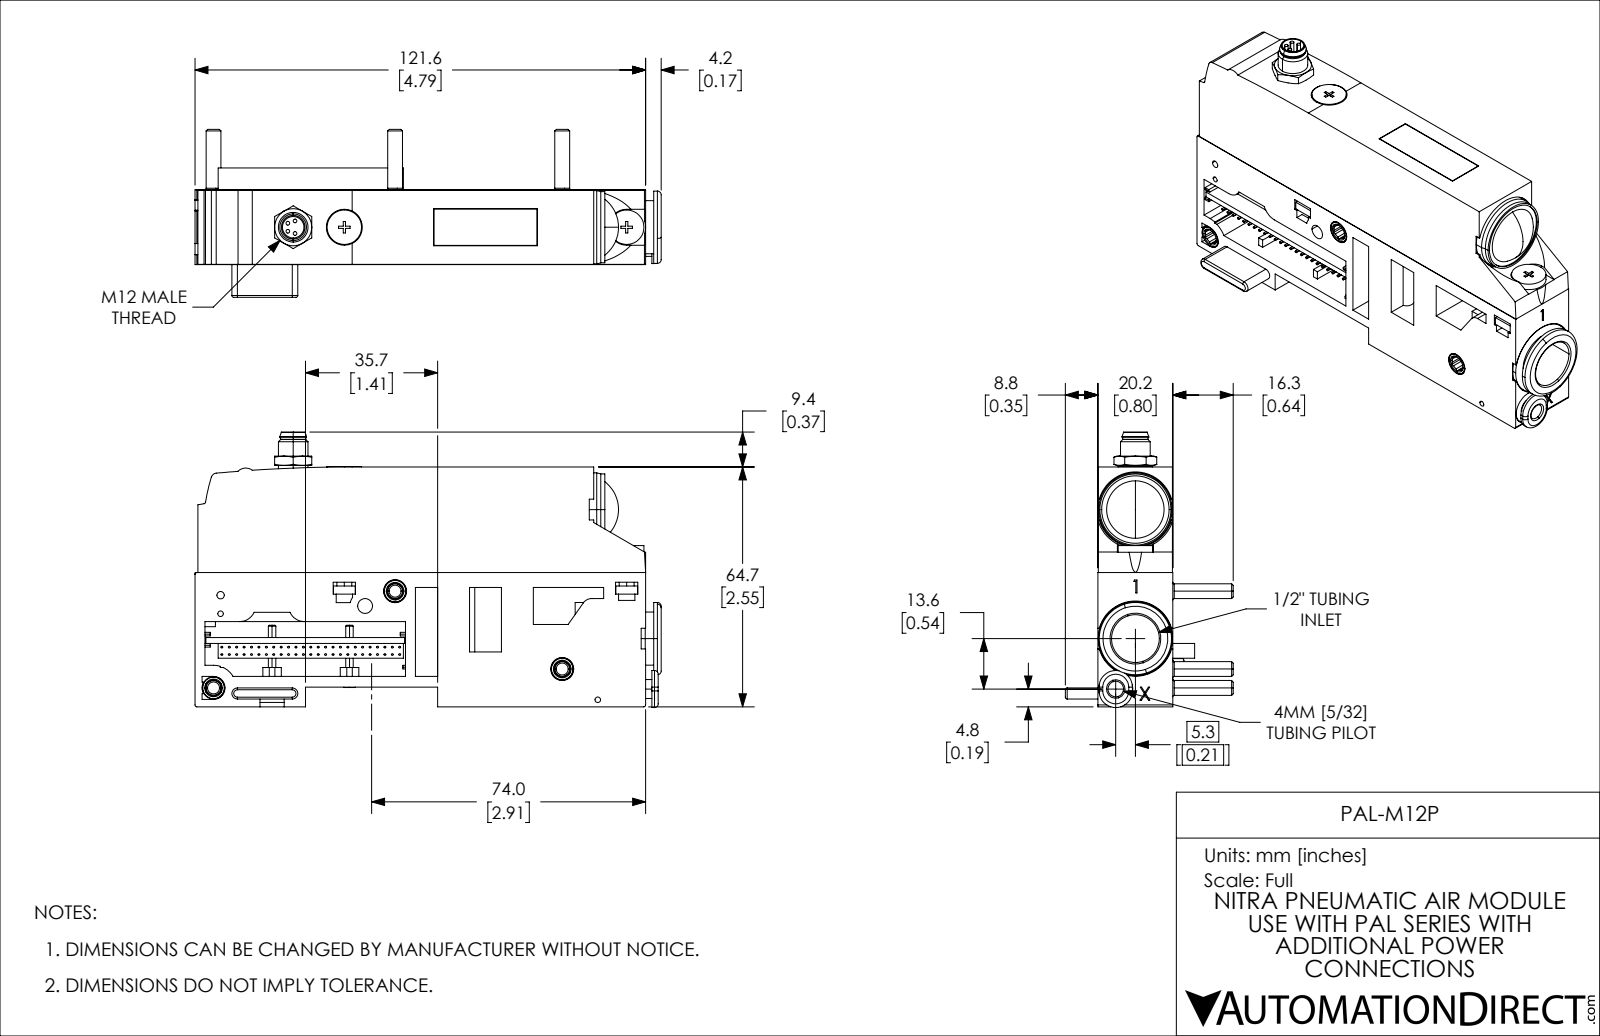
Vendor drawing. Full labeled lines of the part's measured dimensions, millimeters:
Part name (STEP PRODUCT): PAL-M12P
STEP written by: SolidWorks 2019 (CONFIG_CONTROL_DESIGN)
Units: millimetres
Bodies: 4 solids, 1548 faces (1041 planar, 421 cylindrical, 86 other)
Overall size (bounding box): 125.8 × 74.3 × 45.3
Volume: 125 400 mm³ · Surface area: 41 910 mm²
Round holes (diameter × count): ⌀0.5 ×50, ⌀3.3 ×3, ⌀4 ×3, ⌀4.2 ×3, ⌀1.5 ×2, ⌀2 ×2, ⌀2.4 ×2, ⌀4.5 ×2, ⌀6.2 ×2, ⌀3.2 ×1, ⌀4.8 ×1, ⌀5.8 ×1
Round bosses / shafts (diameter × count): ⌀4 ×7, ⌀1 ×4, ⌀9.3 ×3, ⌀6 ×3, ⌀2 ×2, ⌀20 ×1, ⌀19.8 ×1, ⌀19.5 ×1
Partial cylindrical surfaces — rounded edges, fillets, slot ends (radius × count): R0.2 ×12, R0.5 ×11, R0.2 ×8, R0.2 ×4, R1 ×4, R1.5 ×3, R2.1 ×3, R0.8 ×2
Main face-to-face distances: 20.1, 20, 20.2, 64.7, 8.2, 17.7, 17.1, 5.9, 14.8, 41.7
Hole centre spacings: 2, 2.8, 4, 4.5, 6, 6.3, 8, 8.3
